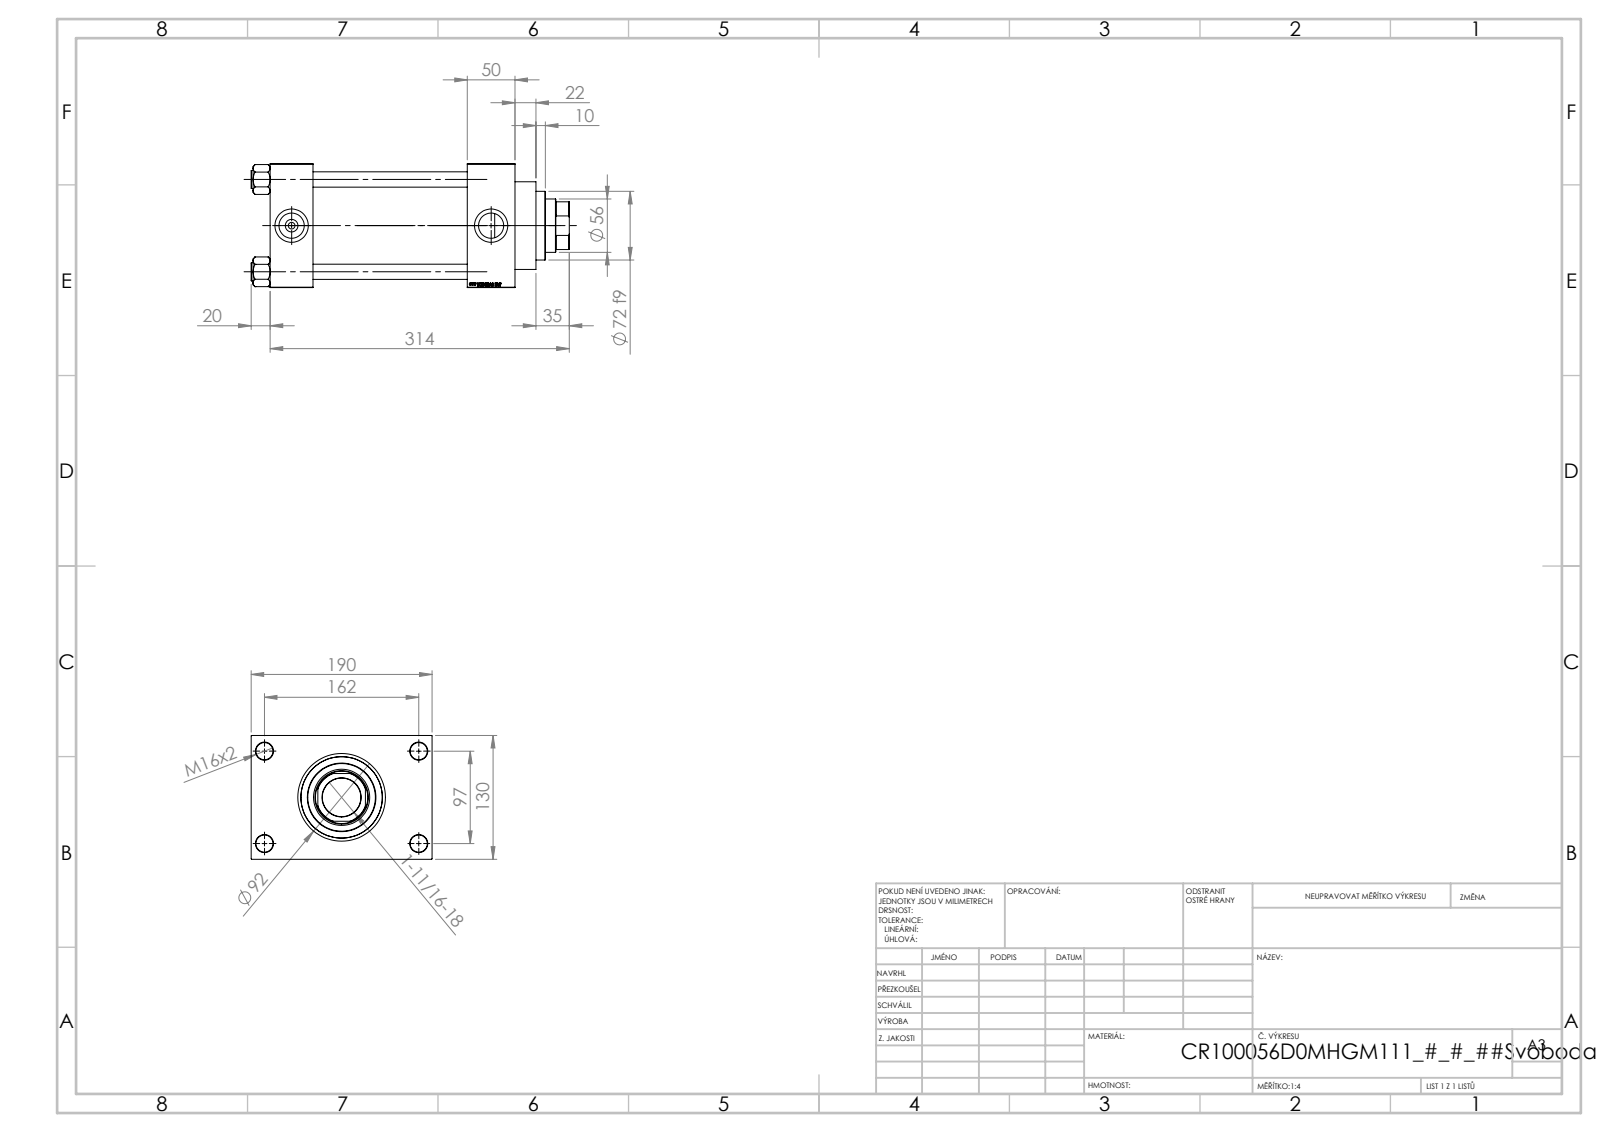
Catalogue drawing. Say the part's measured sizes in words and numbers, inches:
The part is named "NUT_M5_D; V215CR_D_Body; V215CR_VCP_D; V215_VC_A (+1 more)". Its 3-D file was written by "SolidWorks 2019 (CONFIG_CONTROL_DESIGN)". It is 11 solids with 1151 faces: 545 planar, 88 cylindrical and 518 other. Overall it measures 13.15 by 7.48 by 5.118 inches. Its volume is 183.9 cubic inches and its surface area 706.1 square inches. Round holes: 4 of diameter 0.63, 4 of diameter 0.709, 2 of diameter 0.276, 2 of diameter 1.041, 2 of diameter 1.378, 1 of diameter 1.594, 1 of diameter 2.205, 1 of diameter 2.323, 1 of diameter 2.992, 1 of diameter 3.366, 1 of diameter 3.937. Round bosses or shafts: 4 of diameter 0.748, 1 of diameter 4.173, 1 of diameter 3.622, 1 of diameter 2.835. Partial cylindrical surfaces (rounded edges, fillets, slot ends): 1 of radius 1.063. The main face-to-face distances are 5.118, 1.969, 1.772, 8.15, 6.378, 10.118, 8.346, 1.181, 6.299, 7.48. The hole center spacings are 1.281, 2.698, 3.717, 3.815, 4.026, 5.096, 6.367, 3.819.
